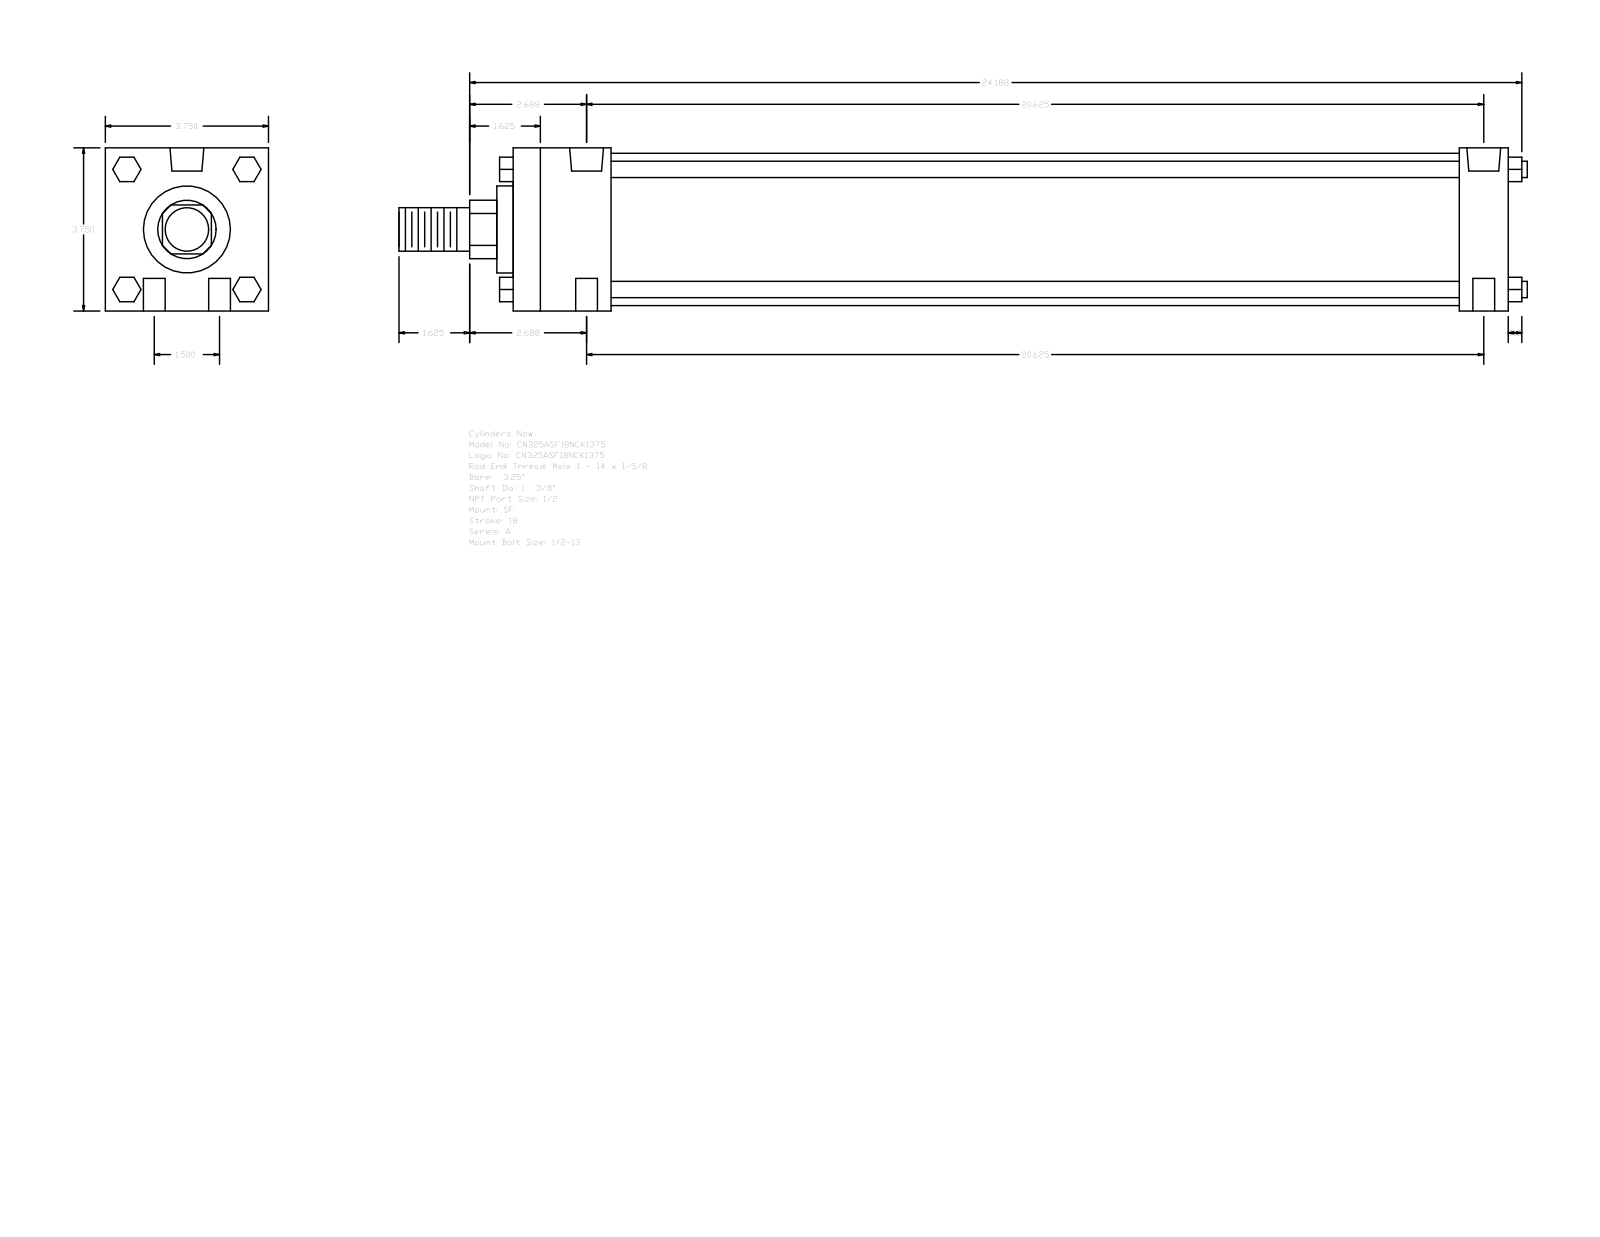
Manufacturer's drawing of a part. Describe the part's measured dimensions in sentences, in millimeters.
The part is named "A_SF__0325_1.375". Its 3-D file was written by "GSSL Pune (CONFIG_CONTROL_DESIGN)". It is 0 solids with 124 faces: 94 planar, 30 cylindrical and 0 other. Overall it measures 658.81 by 95.25 by 95.25 millimeters. Round holes: 4 of diameter 12.7, 2 of diameter 8.73, 2 of diameter 19.77. Round bosses or shafts: 4 of diameter 9.53, 1 of diameter 88.9, 1 of diameter 50.8, 1 of diameter 34.92, 1 of diameter 25.4. Partial cylindrical surfaces (rounded edges, fillets, slot ends): 1 of radius 17.06. The main face-to-face distances are 95.24, 581.02, 57.15, 552.45, 28.57, 495.3, 523.87, 66.67, 9.52, 561.97. The hole center spacings are 19.05, 524.23, 523.88, 38.1, 525.26, 517.52.
